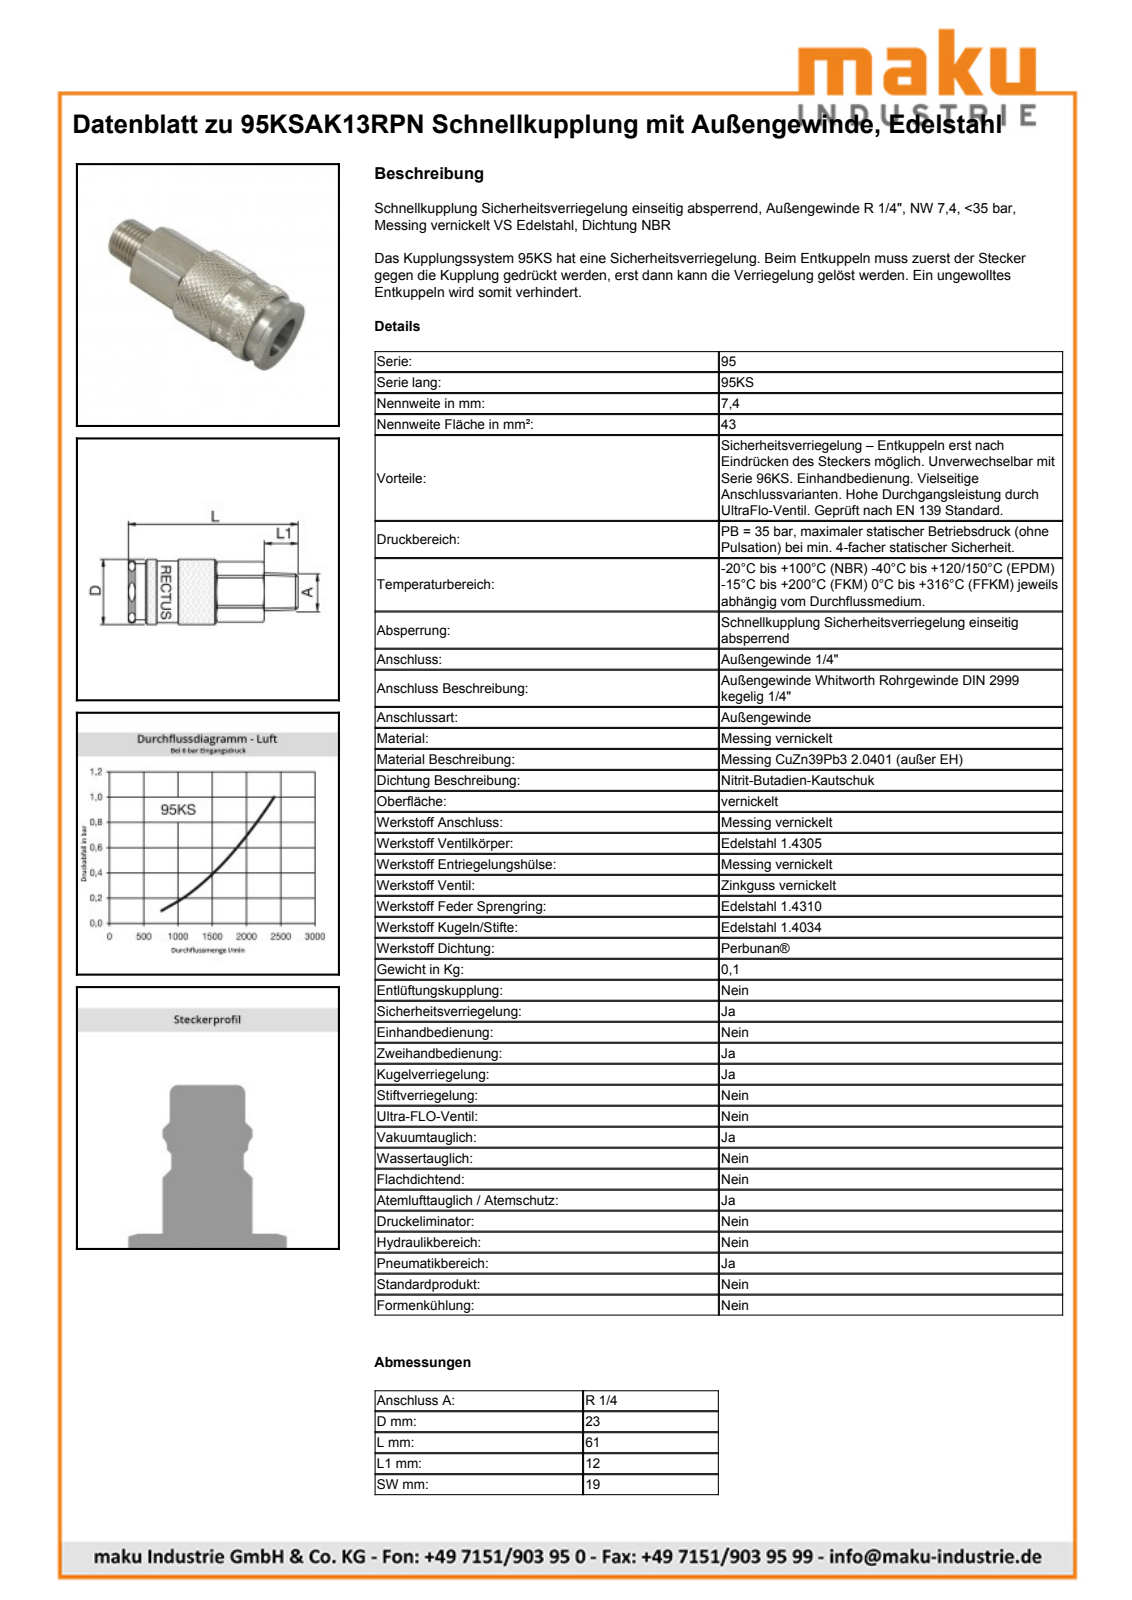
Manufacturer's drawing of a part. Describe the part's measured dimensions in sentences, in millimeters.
The part is named "D110983". Its 3-D file was written by "Autodesk Inventor 2013 (AUTOMOTIVE_DESIGN)". It is 1 solid with 326 faces: 118 planar, 49 cylindrical and 159 other. Overall it measures 59.85 by 23.15 by 23.15 millimeters. Its volume is 17 840 cubic millimeters and its surface area 7 617 square millimeters. Round holes: 1 of diameter 17.25, 1 of diameter 17.9, 1 of diameter 19.35, 1 of diameter 20. Round bosses or shafts: 1 of diameter 23.15, 1 of diameter 22, 1 of diameter 18.95, 1 of diameter 16.32. Partial cylindrical surfaces (rounded edges, fillets, slot ends): 1 of radius 10.7, 1 of radius 10.9. The main face-to-face distances are 19, 47.85, 59.85, 12, 30.8, 17.05, 29.05, 17.3, 13.5, 30.55.
